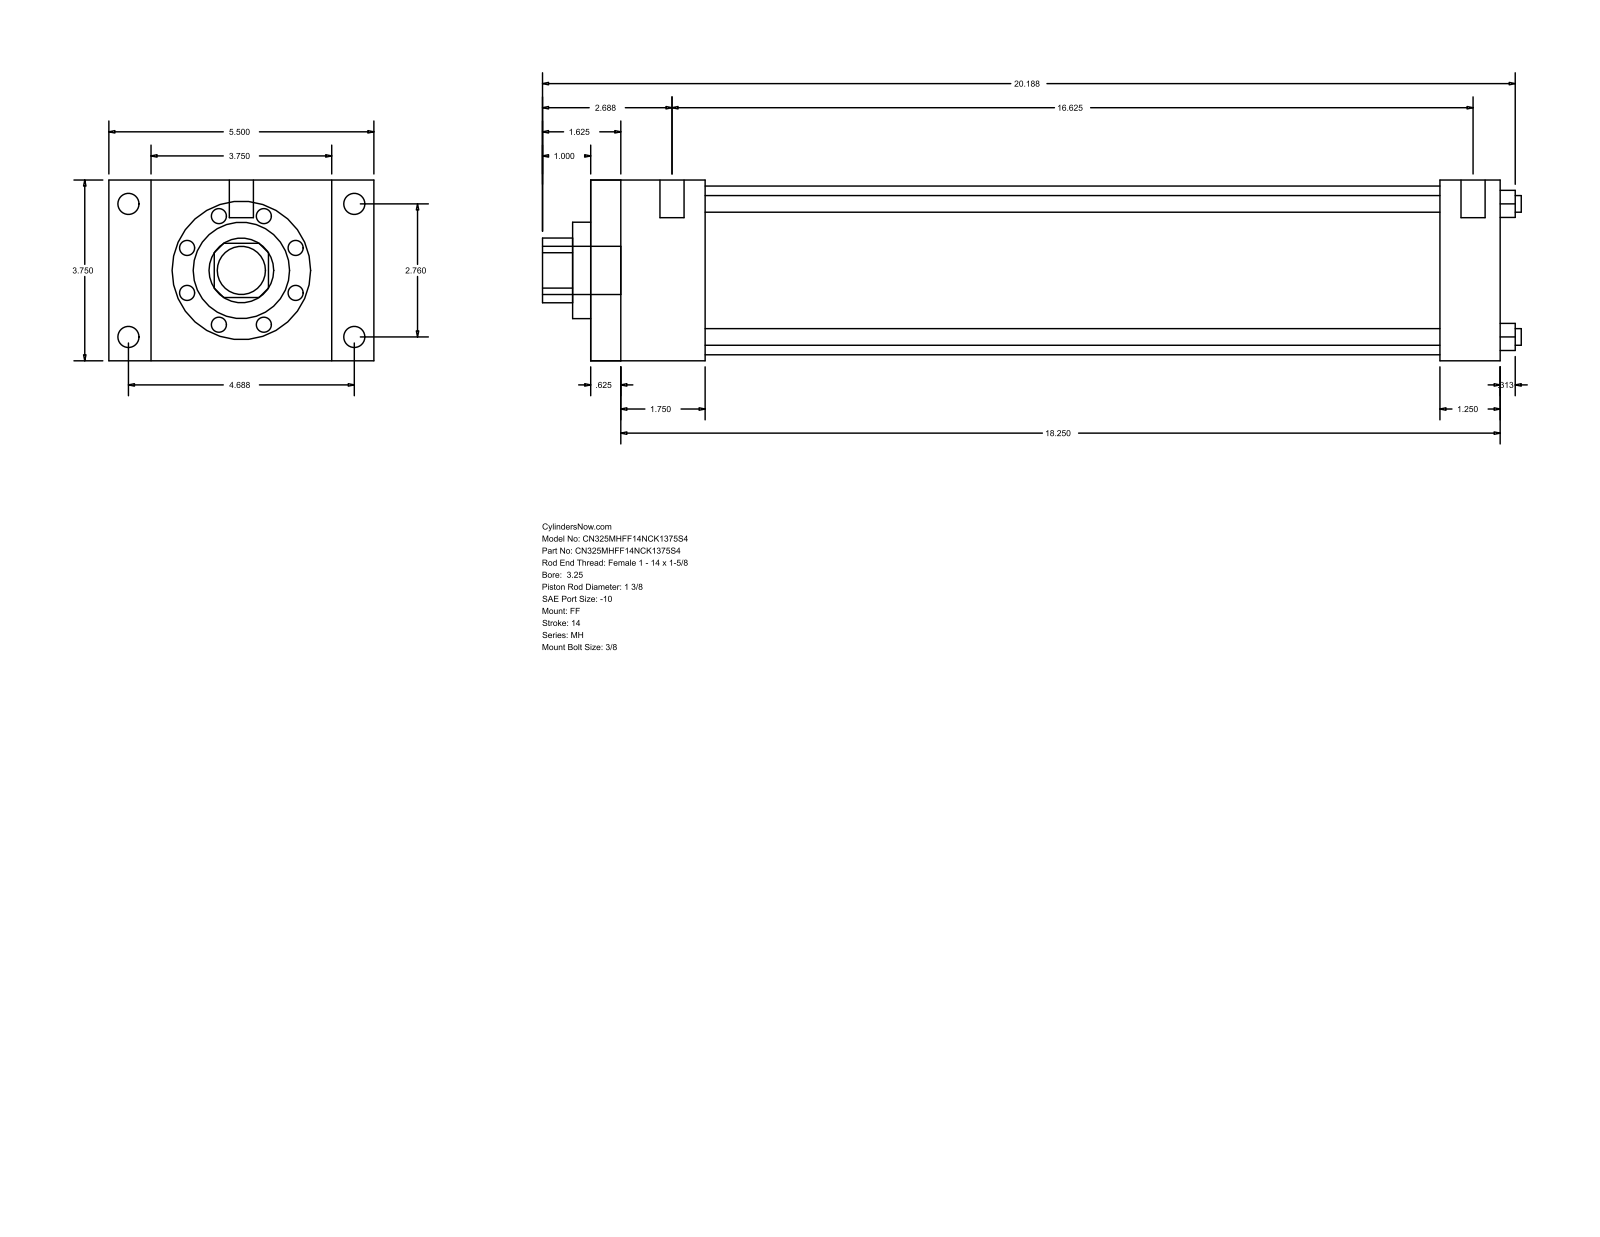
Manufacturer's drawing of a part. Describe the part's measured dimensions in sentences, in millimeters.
The part is named "MH_FF__0325_1.375". Its 3-D file was written by "GSSL Pune (CONFIG_CONTROL_DESIGN)". It is 0 solids with 92 faces: 64 planar, 28 cylindrical and 0 other. Overall it measures 515.94 by 139.7 by 95.25 millimeters. Round holes: 4 of diameter 8.76, 1 of diameter 34.92, 1 of diameter 50.8, 1 of diameter 88.9. Round bosses or shafts: 4 of diameter 11.13, 4 of diameter 5.56, 2 of diameter 12.7, 1 of diameter 25.4. Partial cylindrical surfaces (rounded edges, fillets, slot ends): 1 of radius 17.06. The main face-to-face distances are 95.24, 479.42, 15.87, 463.55, 22.23, 117.47, 447.67, 431.8, 31.75, 60.32. The hole center spacings are 49.57, 70.1, 99.14.
